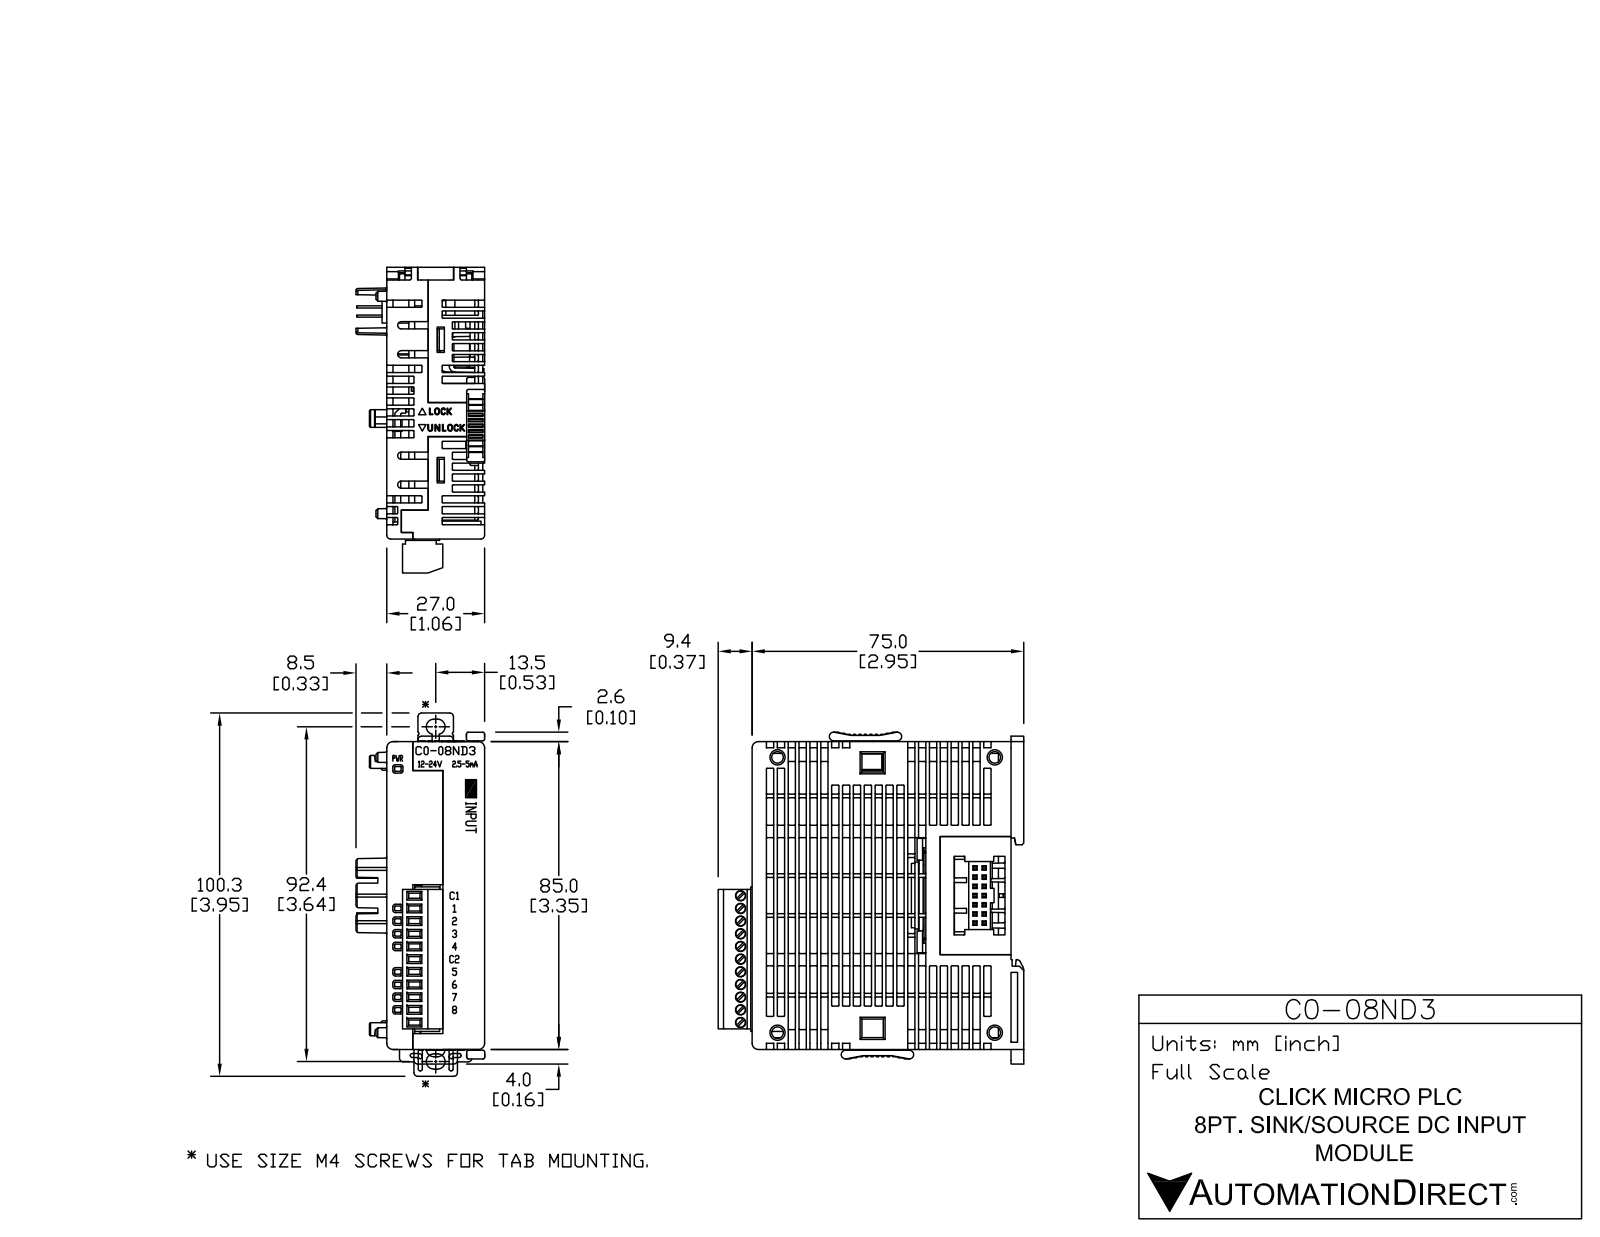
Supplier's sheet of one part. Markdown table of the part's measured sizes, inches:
| quantity | value |
| --- | --- |
| part name | C0-08ND3 |
| STEP written by | SolidWorks 2009 (AUTOMOTIVE_DESIGN) |
| units | inches |
| bodies | 1 solid, 3689 faces (2637 planar, 968 cylindrical, 84 other) |
| overall size | 3.606 × 3.323 × 1.4 |
| volume | 9.917 in³ |
| surface area | 49.24 in² |
| round holes (diameter × count) | 0.039 × 11, 0.11 × 11, 0.126 × 4, 0.079 × 2 |
| round bosses / shafts (diameter × count) | 0.102 × 11, 0.075 × 1 |
| partial cylindrical surfaces (radius × count) | 0.008 × 570, 0.02 × 43, 0.012 × 22, 0.039 × 18, 0.047 × 12, 0.11 × 11, 0.067 × 6, 0.083 × 4 |
| main face-to-face distances | 1.063, 0.02, 0.02, 1.043, 2.815, 0.067, 3.346, 1.035, 1.056, 3.327 |
| hole center spacings | 0.138, 0.276, 0.413, 0.551, 0.689, 0.827, 0.965, 1.102 |
